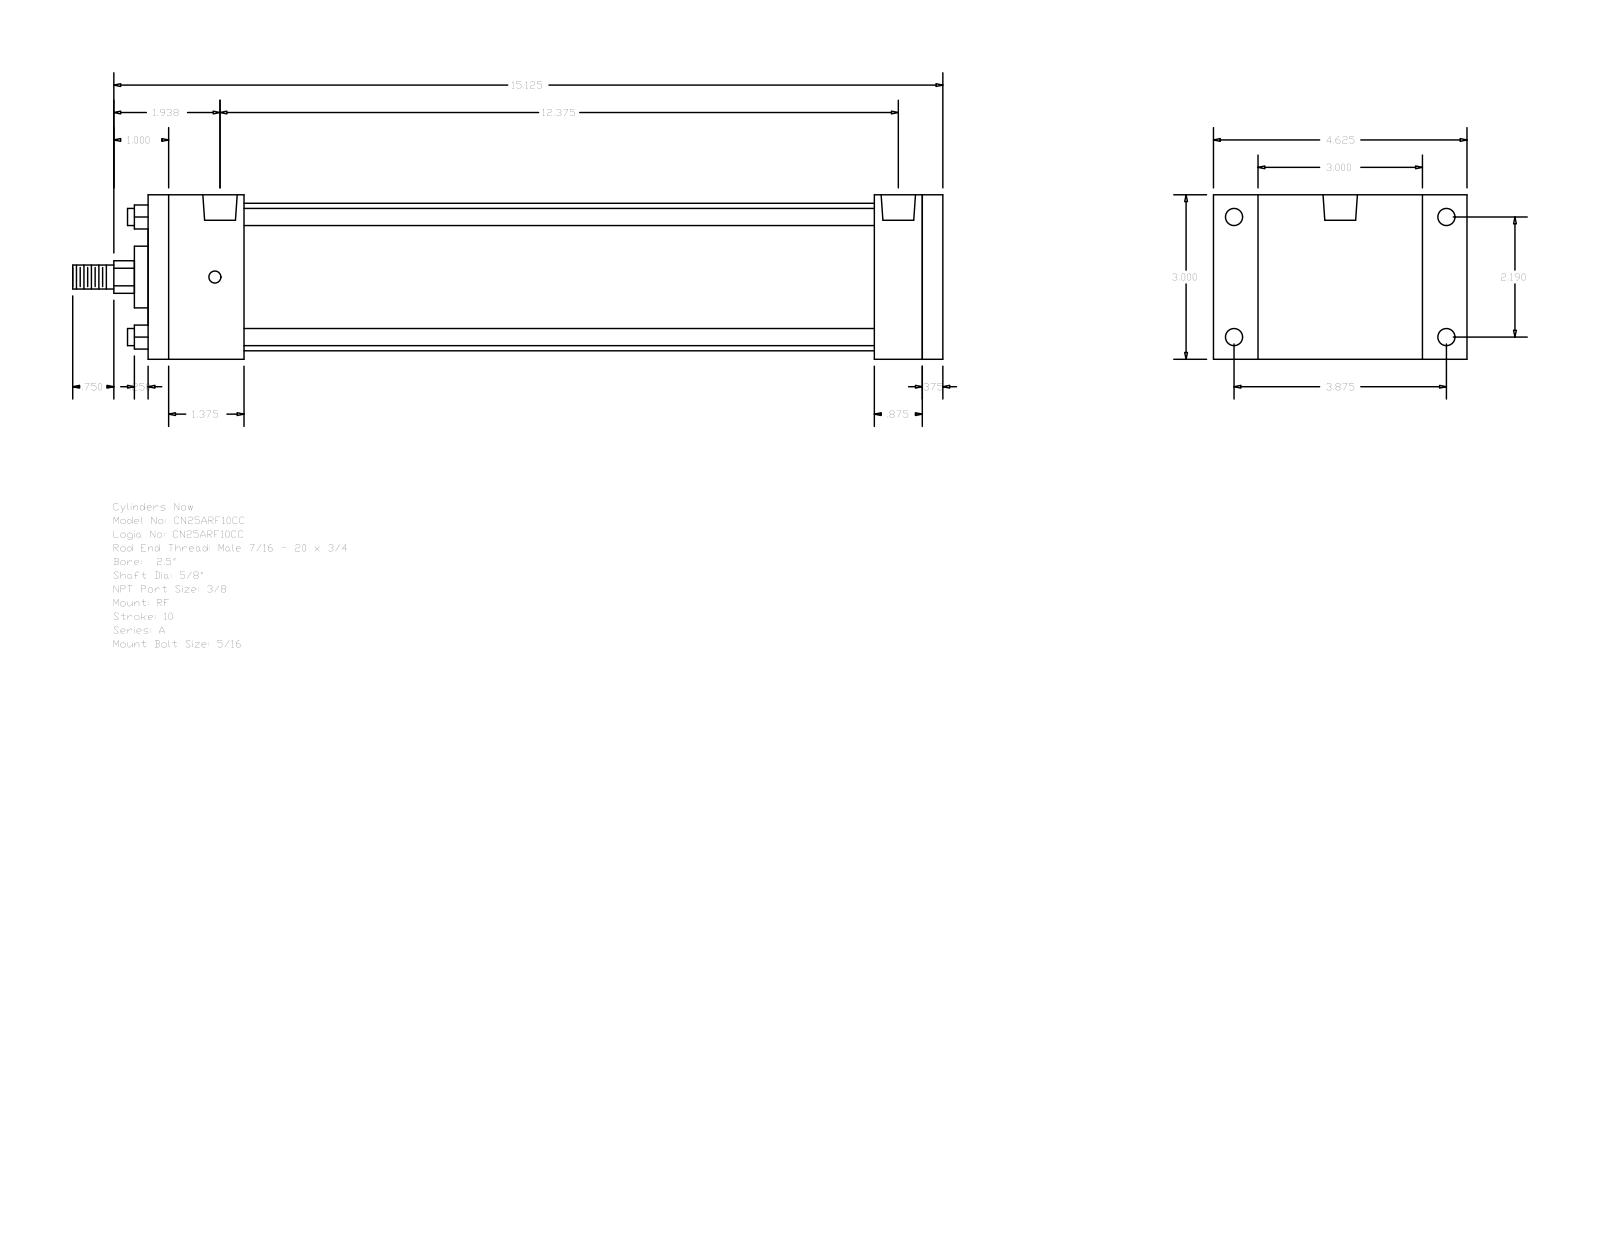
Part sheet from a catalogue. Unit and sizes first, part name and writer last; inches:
Units: inches
Overall size (bounding box): 15.875 × 4.625 × 3
Round holes (diameter × count): ⌀0.219 ×4, ⌀0.313 ×4, ⌀0.627 ×2
Round bosses / shafts (diameter × count): ⌀0.313 ×4, ⌀2.69 ×1, ⌀1.125 ×1, ⌀0.625 ×1, ⌀0.437 ×1
Partial cylindrical surfaces — rounded edges, fillets, slot ends (radius × count): R0.297 ×1
Main face-to-face distances: 3, 14.5, 0.375, 14.125, 1.75, 1.25, 13.25, 11.5, 12.375, 12.75
Hole centre spacings: 0.094, 2.19, 3.875, 4.451, 12.469, 12.563, 12.375
Bodies: 0 solids, 92 faces (64 planar, 28 cylindrical, 0 other)
Part name (STEP PRODUCT): A_RF__0250_0.625
STEP written by: GSSL Pune (CONFIG_CONTROL_DESIGN)
